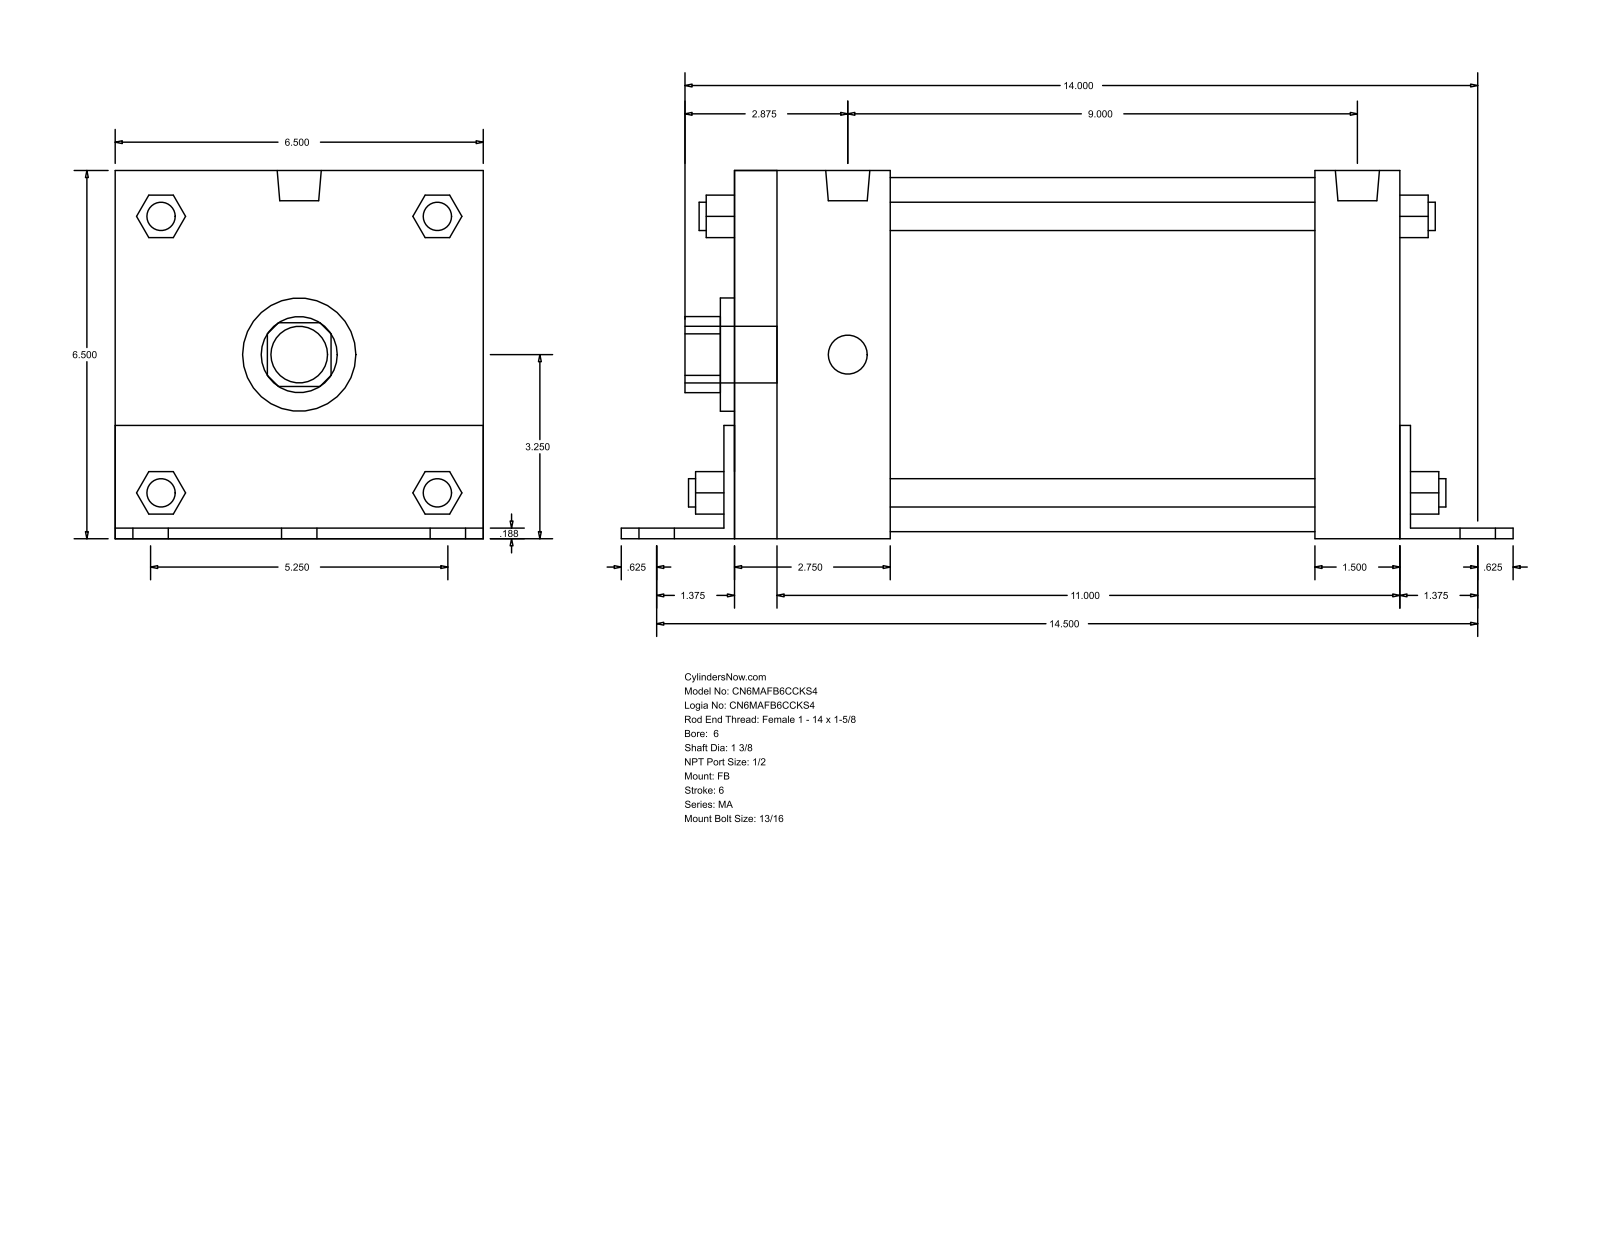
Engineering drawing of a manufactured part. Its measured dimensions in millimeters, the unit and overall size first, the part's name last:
Units: millimetres
Overall size (bounding box): 396.88 × 165.15 × 165.1
Round holes (diameter × count): ⌀34.92 ×1, ⌀50.8 ×1, ⌀158.75 ×1
Round bosses / shafts (diameter × count): ⌀20.64 ×6, ⌀17.46 ×4, ⌀12.7 ×4, ⌀19.77 ×2, ⌀25.4 ×1
Partial cylindrical surfaces — rounded edges, fillets, slot ends (radius × count): R17.06 ×1, R32.05 ×1
Main face-to-face distances: 165.1, 4.76, 295.27, 165.15, 4.71, 160.39, 4.77, 38.1, 300.04, 304.8
Bodies: 0 solids, 140 faces (105 planar, 35 cylindrical, 0 other)
Part name (STEP PRODUCT): MA_FB__0600_1.375
STEP written by: GSSL Pune (CONFIG_CONTROL_DESIGN)
